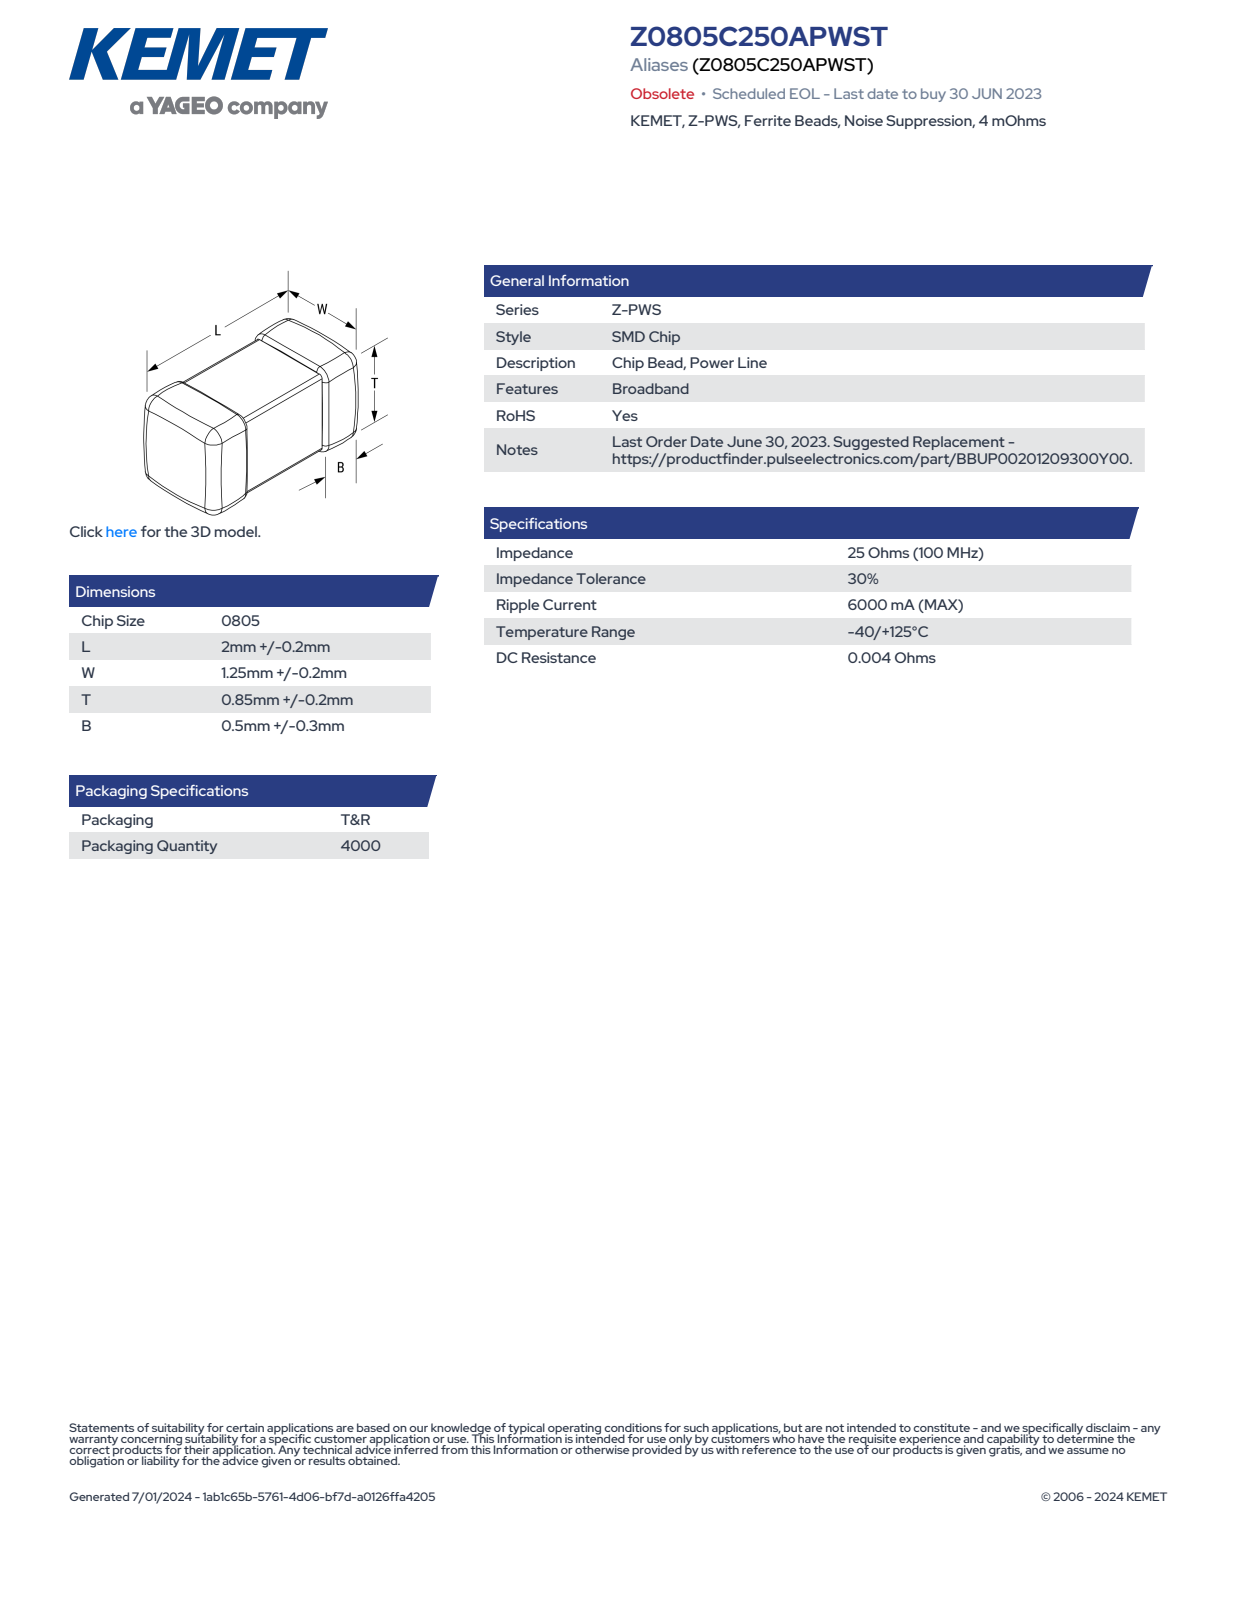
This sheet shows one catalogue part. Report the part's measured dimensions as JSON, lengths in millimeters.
{"part_name": "IS_KC_0805_L2.2W1.45T1.05B0.8", "step_written_by": "SolidWorks 2014 (AUTOMOTIVE_DESIGN)", "units": "millimeters", "bodies": {"solids": 4, "faces": 73, "planar": 73, "cylindrical": 0, "other": 0}, "overall_size": [2.2, 1.45, 1.05], "volume_mm3": 3, "surface_area_mm2": 14, "face_to_face_distances": [1.05, 1.03, 1.45, 2.2, 1.43, 1.01, 1.41, 0.8, 1.4, 1.04]}
